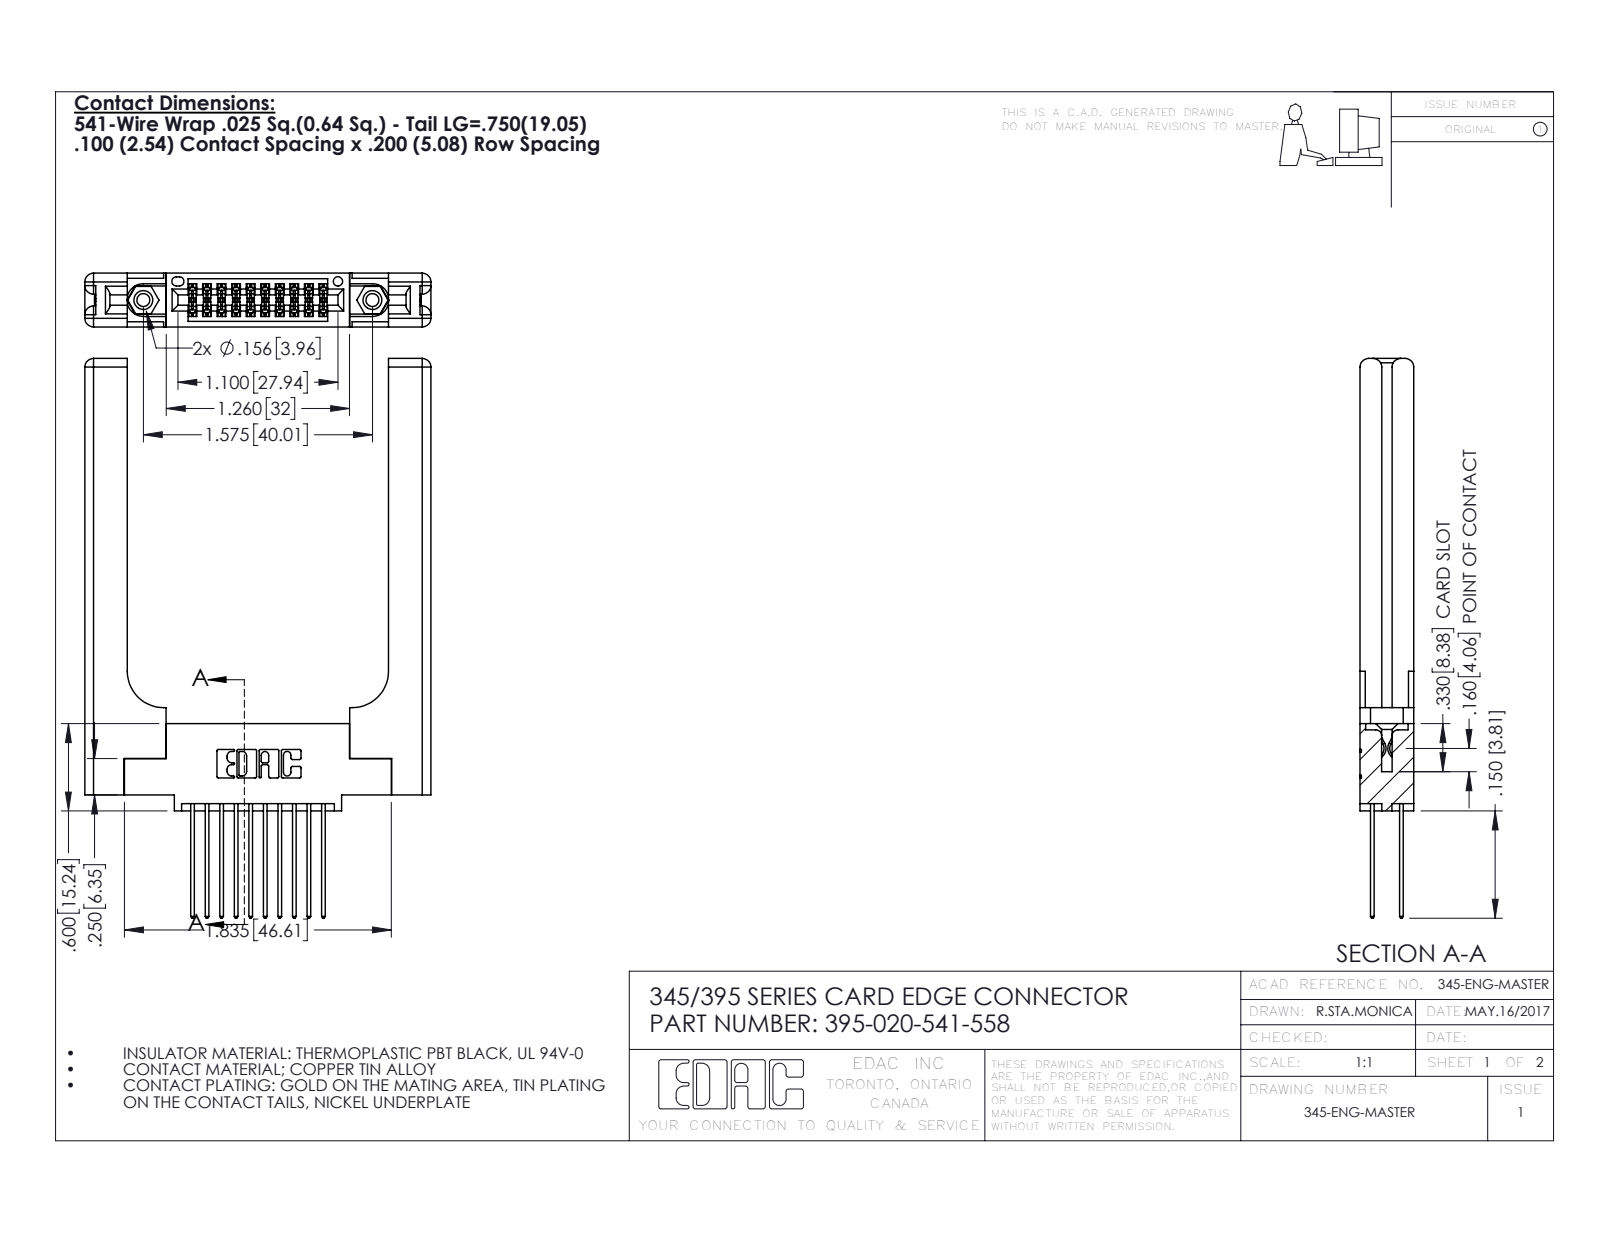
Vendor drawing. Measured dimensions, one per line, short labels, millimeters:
name: 345 Part_0.110 Offset - 0.156 Dia-TH; 345-292-001_345-293-141; 345-220-058_345-220-058; 395-020-541-558 (+1 more)
written by: SolidWorks 2016 (CONFIG_CONTROL_DESIGN)
unit: mm
bodies: 25 solids, 1386 faces (892 planar, 434 cylindrical, 60 other)
size: 97.7 × 60.4 × 9.4
volume: 14 100 mm³; area: 13 370 mm²
holes: 2× ⌀2.3, 2× ⌀3.2, 2× ⌀4, 1× ⌀1.6
bosses: 2× ⌀3.9
rounds: 30× R0.2, 22× R0.3, 20× R0.3, 16× R1.5, 6× R0.2, 6× R0.8, 3× R0.7, 2× R0.4
face distances: 9.4, 1.8, 7.6, 3.8, 3.8, 2, 5.6, 5.1, 2.5, 6.9
hole spacings: 6.9, 34.1, 40
